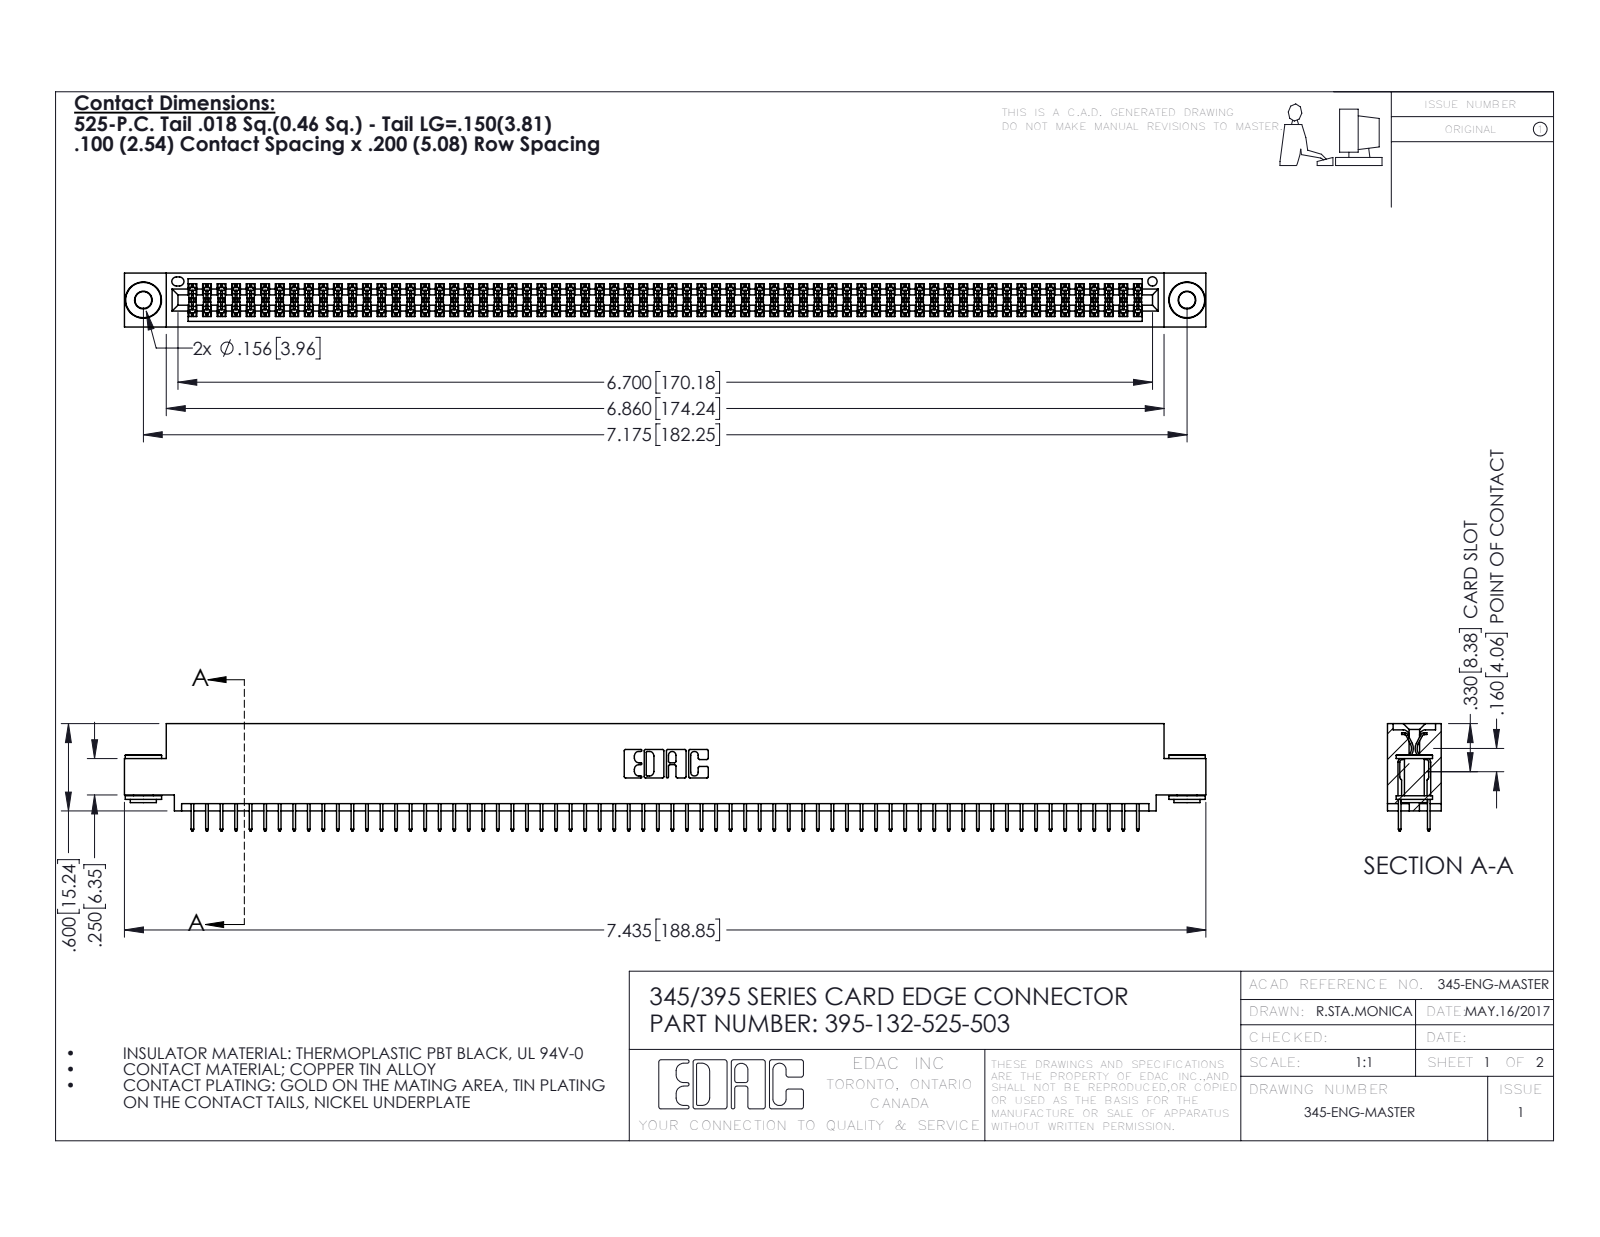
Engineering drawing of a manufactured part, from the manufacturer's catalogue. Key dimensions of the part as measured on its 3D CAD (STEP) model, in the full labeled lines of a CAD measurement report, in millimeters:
Part name (STEP PRODUCT): 345 Part_0.110 Offset - 0.156 Dia-TH; 345-250-002_345-250-002-102; 345-292-001_345-293-125; 395-132-525-503
STEP written by: SolidWorks 2020 (CONFIG_CONTROL_DESIGN)
Units: millimetres
Bodies: 135 solids, 7296 faces (5242 planar, 2046 cylindrical, 8 other)
Overall size (bounding box): 188.8 × 18.7 × 9.4
Volume: 18 300 mm³ · Surface area: 27 150 mm²
Round holes (diameter × count): ⌀2.9 ×2, ⌀4 ×2, ⌀1.6 ×1
Round bosses / shafts (diameter × count): ⌀6.4 ×2, ⌀4.6 ×2, ⌀3.5 ×2
Partial cylindrical surfaces — rounded edges, fillets, slot ends (radius × count): R0.2 ×198, R0.3 ×22, R0.2 ×6, R0.8 ×6, R0.7 ×3, R0.4 ×2, R0.5 ×2, R0.6 ×2
Main face-to-face distances: 1.8, 7.6, 5.1, 9.4, 0.6, 2.5, 6.9, 5.7, 1.8, 4.4
Hole centre spacings: 6.9, 176.3, 182.2
